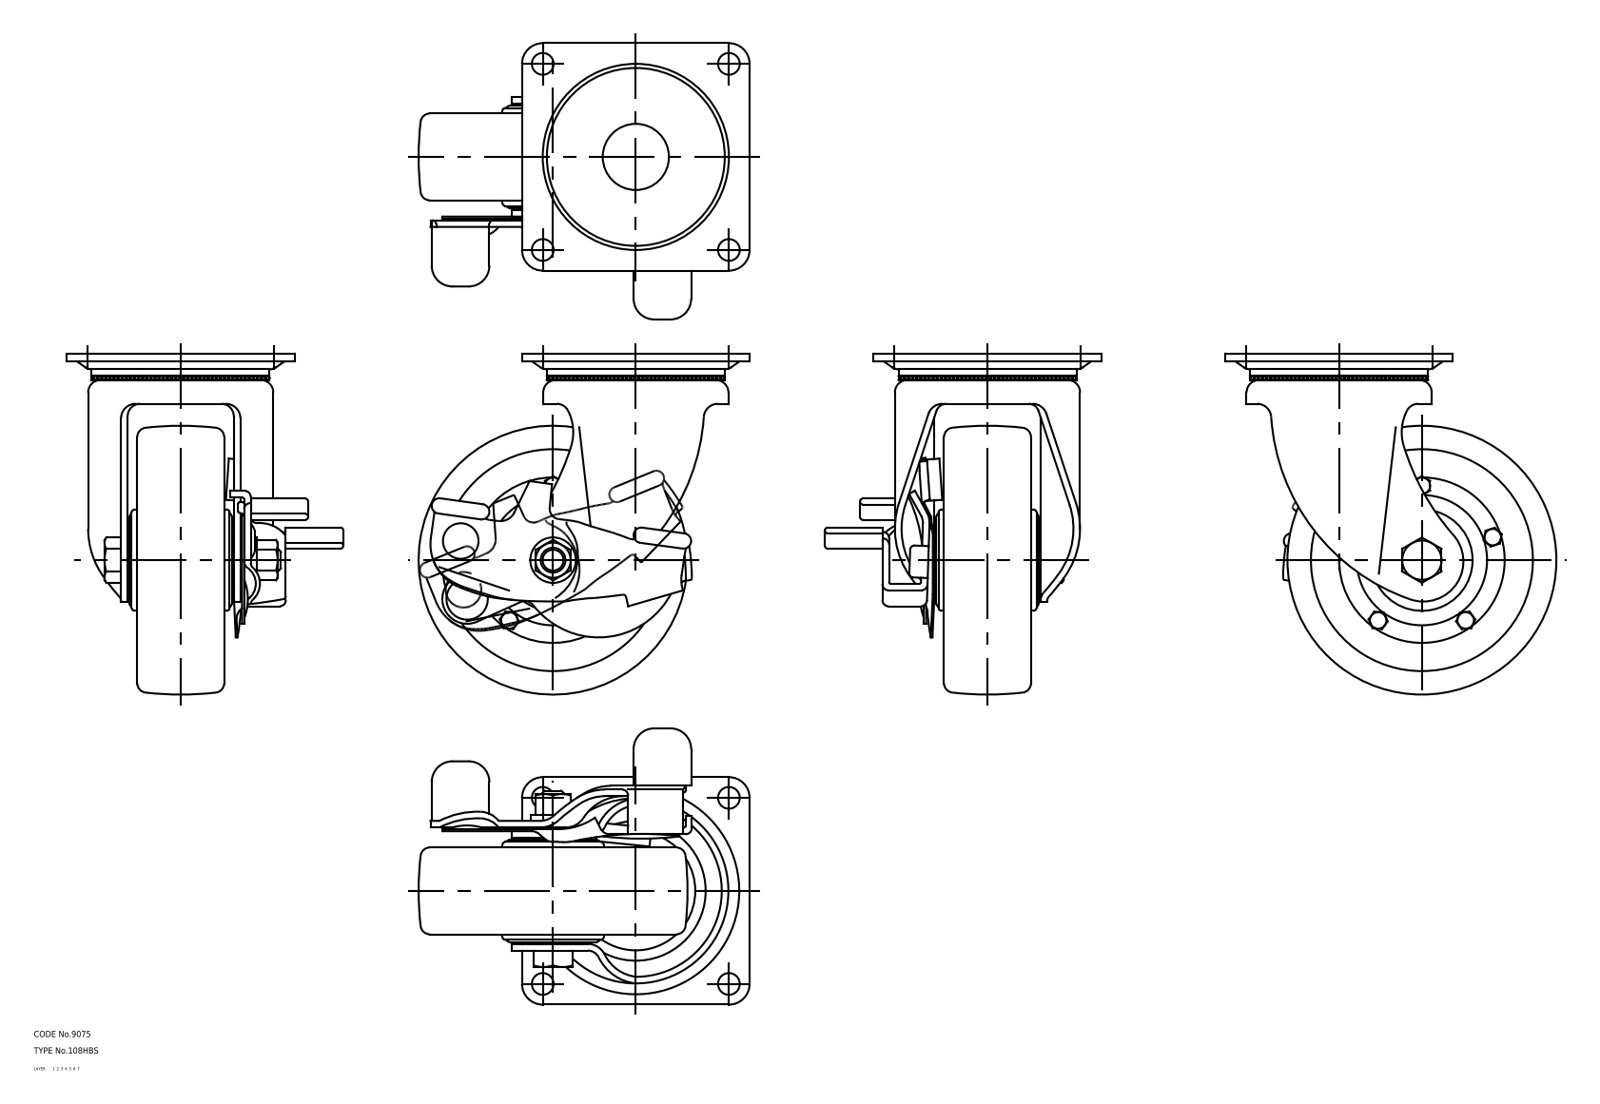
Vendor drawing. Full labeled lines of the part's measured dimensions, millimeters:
Part name (STEP PRODUCT): 67143890; 67143903; 67143916; 67143929 (+3 more)
STEP written by: CADfix (AUTOMOTIVE_DESIGN)
Units: millimetres
Bodies: 7 solids, 605 faces (0 planar, 0 cylindrical, 605 other)
Overall size (bounding box): 165 × 160 × 134.6
Volume: 727 813 mm³ · Surface area: 159 137 mm²
